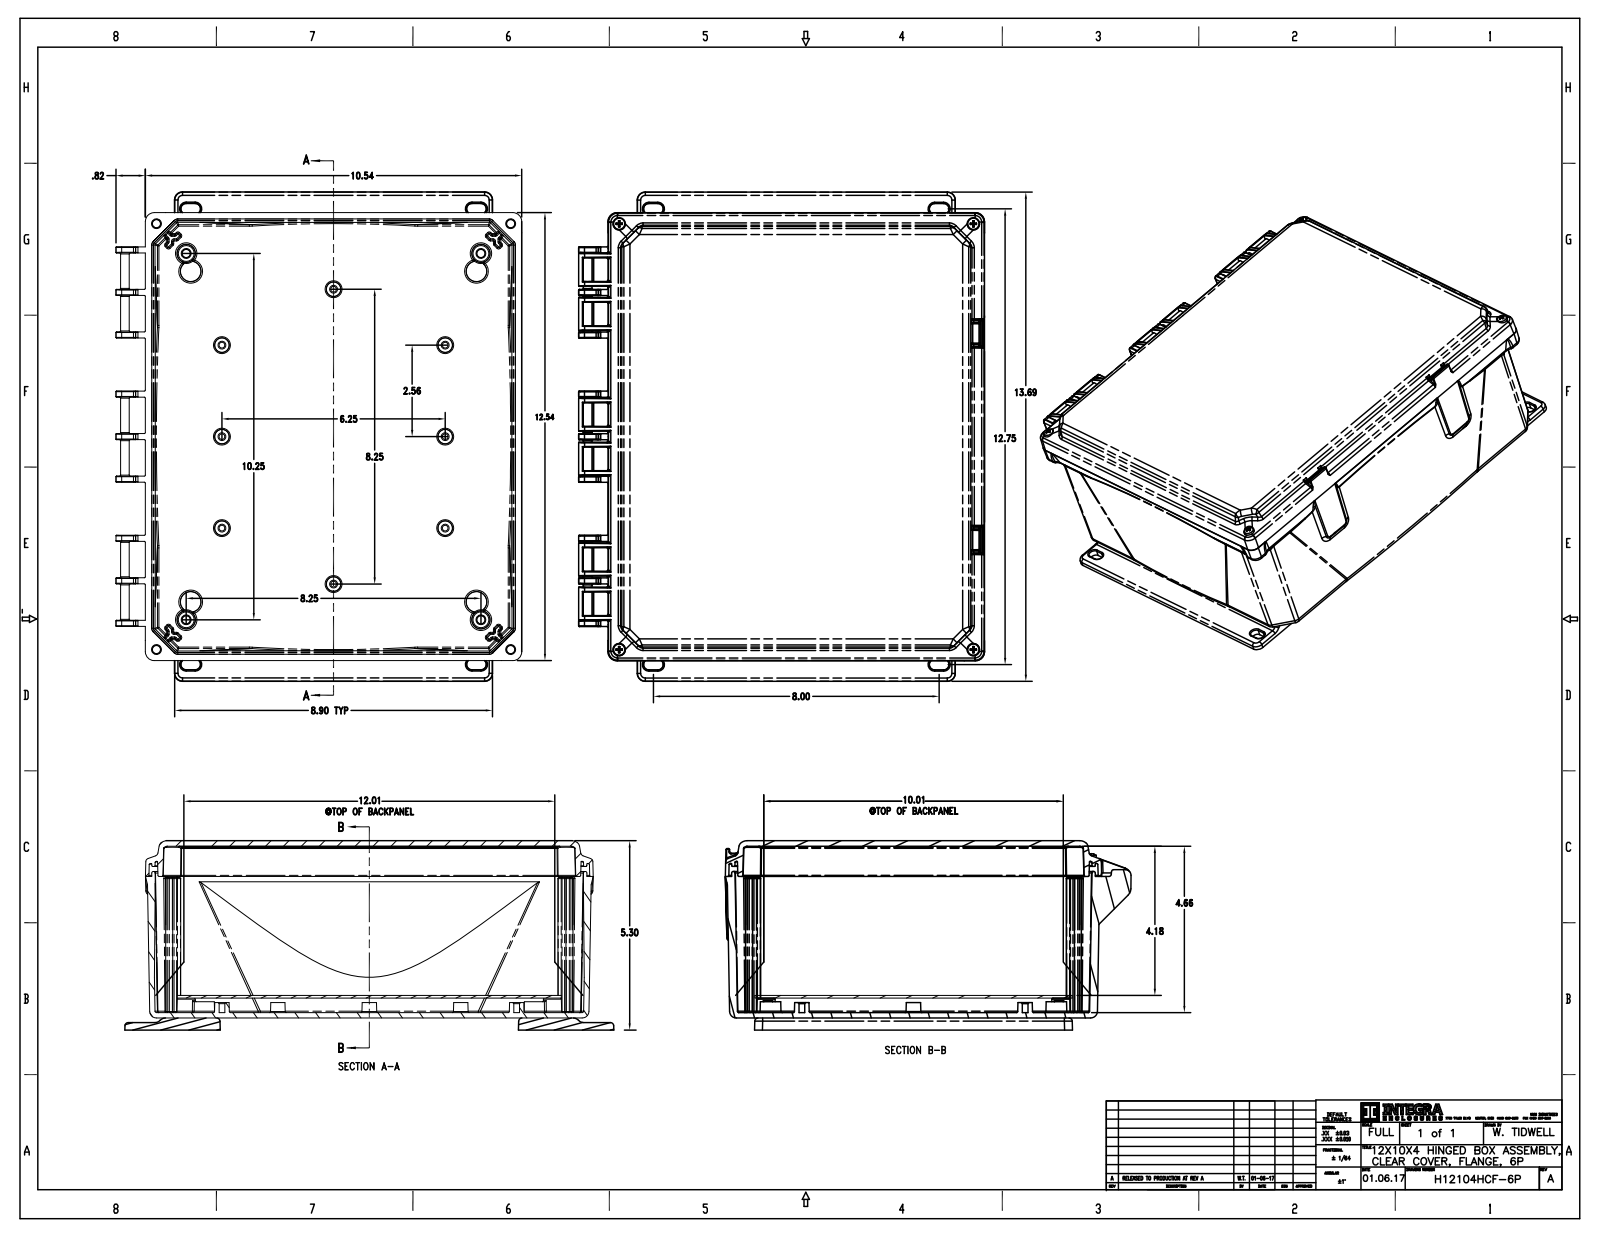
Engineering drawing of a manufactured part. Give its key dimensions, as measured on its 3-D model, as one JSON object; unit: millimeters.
{"part_name": "H12104BH; 9912525-80-10; 9912521-80-10; H12104BH_ASM (+5 more)", "step_written_by": "CREO PARAMETRIC BY PTC INC, 2016050 (CONFIG_CONTROL_DESIGN)", "units": "millimeters", "bodies": {"solids": 24, "faces": 4688, "planar": 1194, "cylindrical": 1808, "other": 1686}, "overall_size": [347.7, 288.5, 134.6], "volume_mm3": 1469000, "surface_area_mm2": 762600, "round_holes": [[4.1, 8], [4.8, 8], [5.1, 4], [9.1, 4]], "round_bosses_or_shafts": [[6.4, 12], [7.6, 8], [7.6, 8], [7.4, 8], [6.6, 8], [6.6, 8], [9.5, 4], [9.4, 4]], "partial_cylinders_radius": [[0.8, 421], [0.5, 153], [0.4, 91], [1, 79], [0.1, 48], [2.3, 36], [2.5, 28], [0.3, 26]], "face_to_face_distances": [3.8, 12.4, 3, 96.8, 103.6, 100.6, 6.9, 10, 8.6, 2.5], "hole_center_spacings": [13.1, 29.9, 41.7, 57, 65, 69.9, 88.8, 98.1]}
